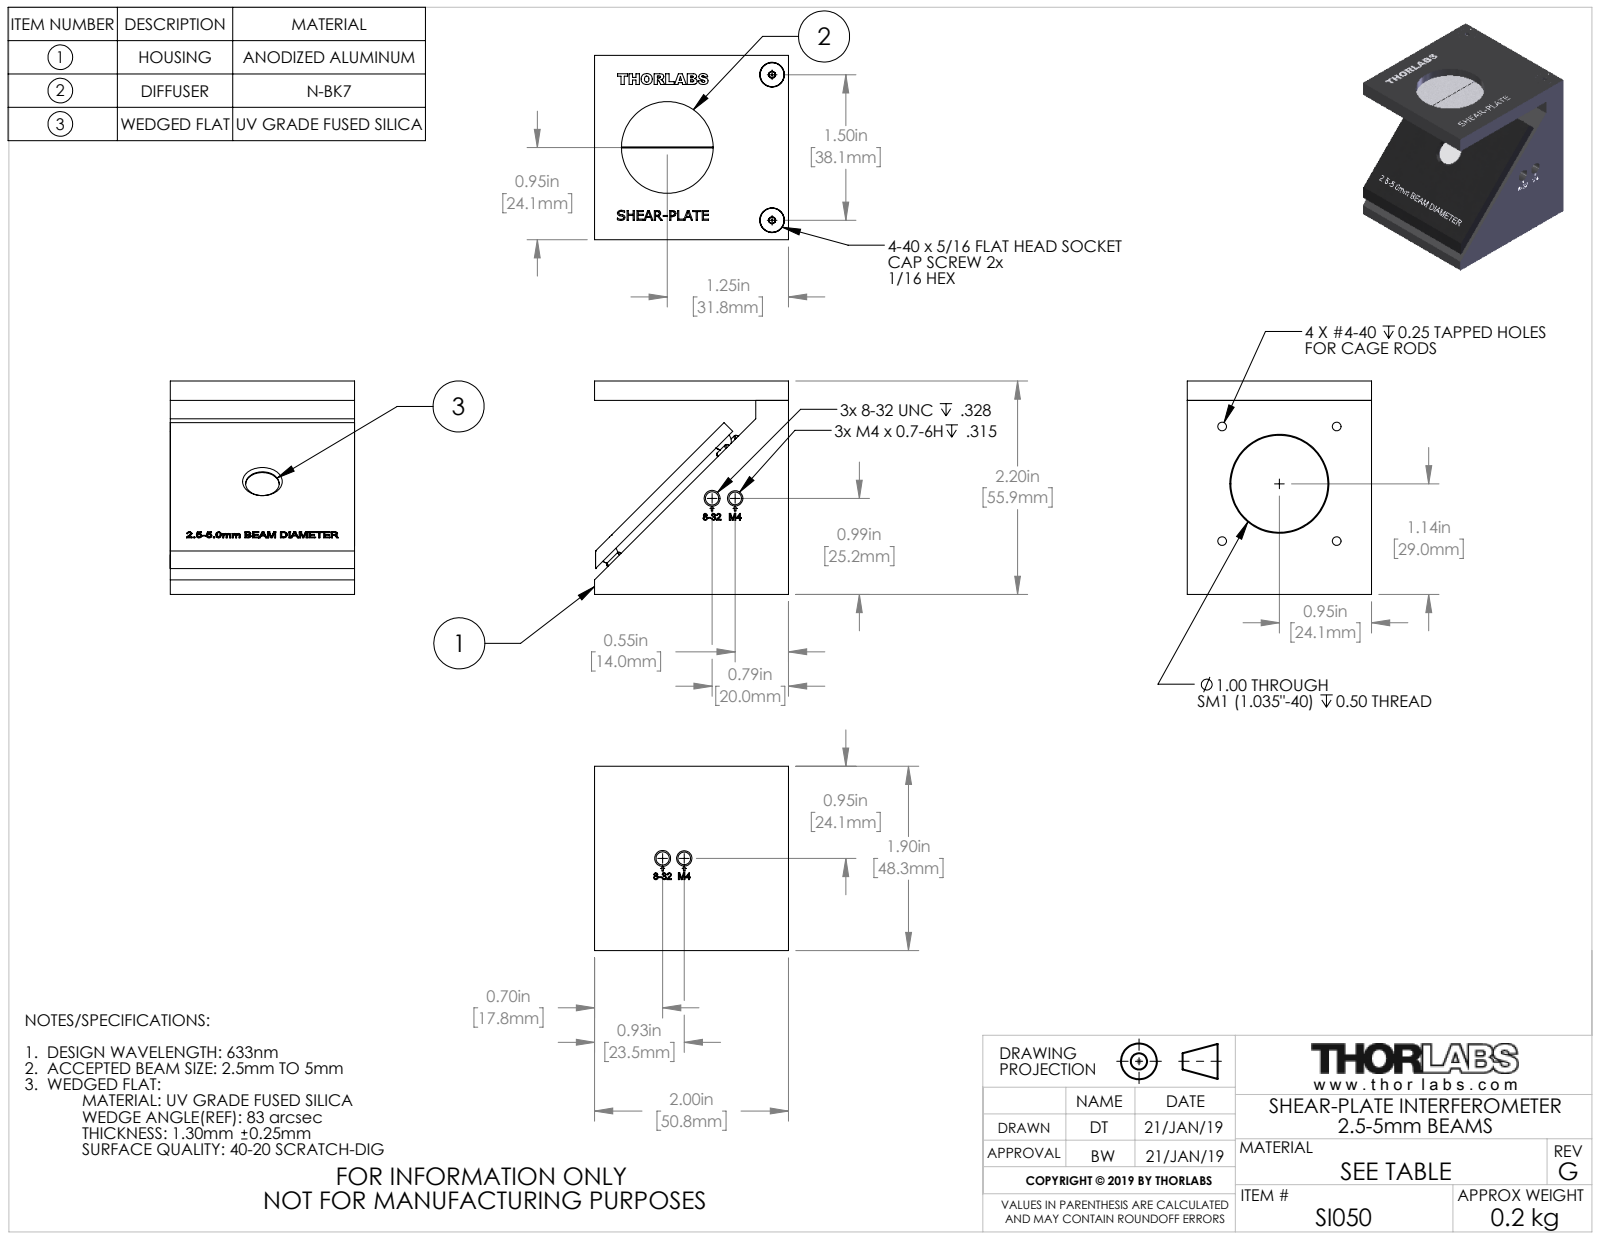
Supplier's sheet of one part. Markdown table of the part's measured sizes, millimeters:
| quantity | value |
| --- | --- |
| part name | 16649-E0W |
| STEP written by | SolidWorks 2018 (CONFIG_CONTROL_DESIGN) |
| units | millimeters |
| bodies | 19 solids, 1145 faces (554 planar, 193 cylindrical, 398 other) |
| overall size | 55.9 × 50.8 × 48.3 |
| volume | 74 150 mm³ |
| surface area | 27 200 mm² |
| round holes (diameter × count) | 2.3 × 6, 1.6 × 3, 3.1 × 3, 3.5 × 3, 3.6 × 3, 4.2 × 3, 4.7 × 3, 3.3 × 2, 3.3 × 2, 4 × 2, 8.8 × 1, 12.8 × 1 |
| round bosses / shafts (diameter × count) | 2.4 × 16, 1.6 × 6, 3.2 × 2, 2.8 × 2, 25.4 × 1, 12.7 × 1, 3.2 × 1 |
| partial cylindrical surfaces (radius × count) | 0.8 × 12, 1.2 × 4 |
| main face-to-face distances | 50.8, 3.3, 55.9, 5.1, 48.3, 5.2, 1.9, 8.7, 5.5, 3.5 |
| hole center spacings | 21.2, 30, 45.5, 25.3, 25.4, 29.9, 33.4, 34.4 |
